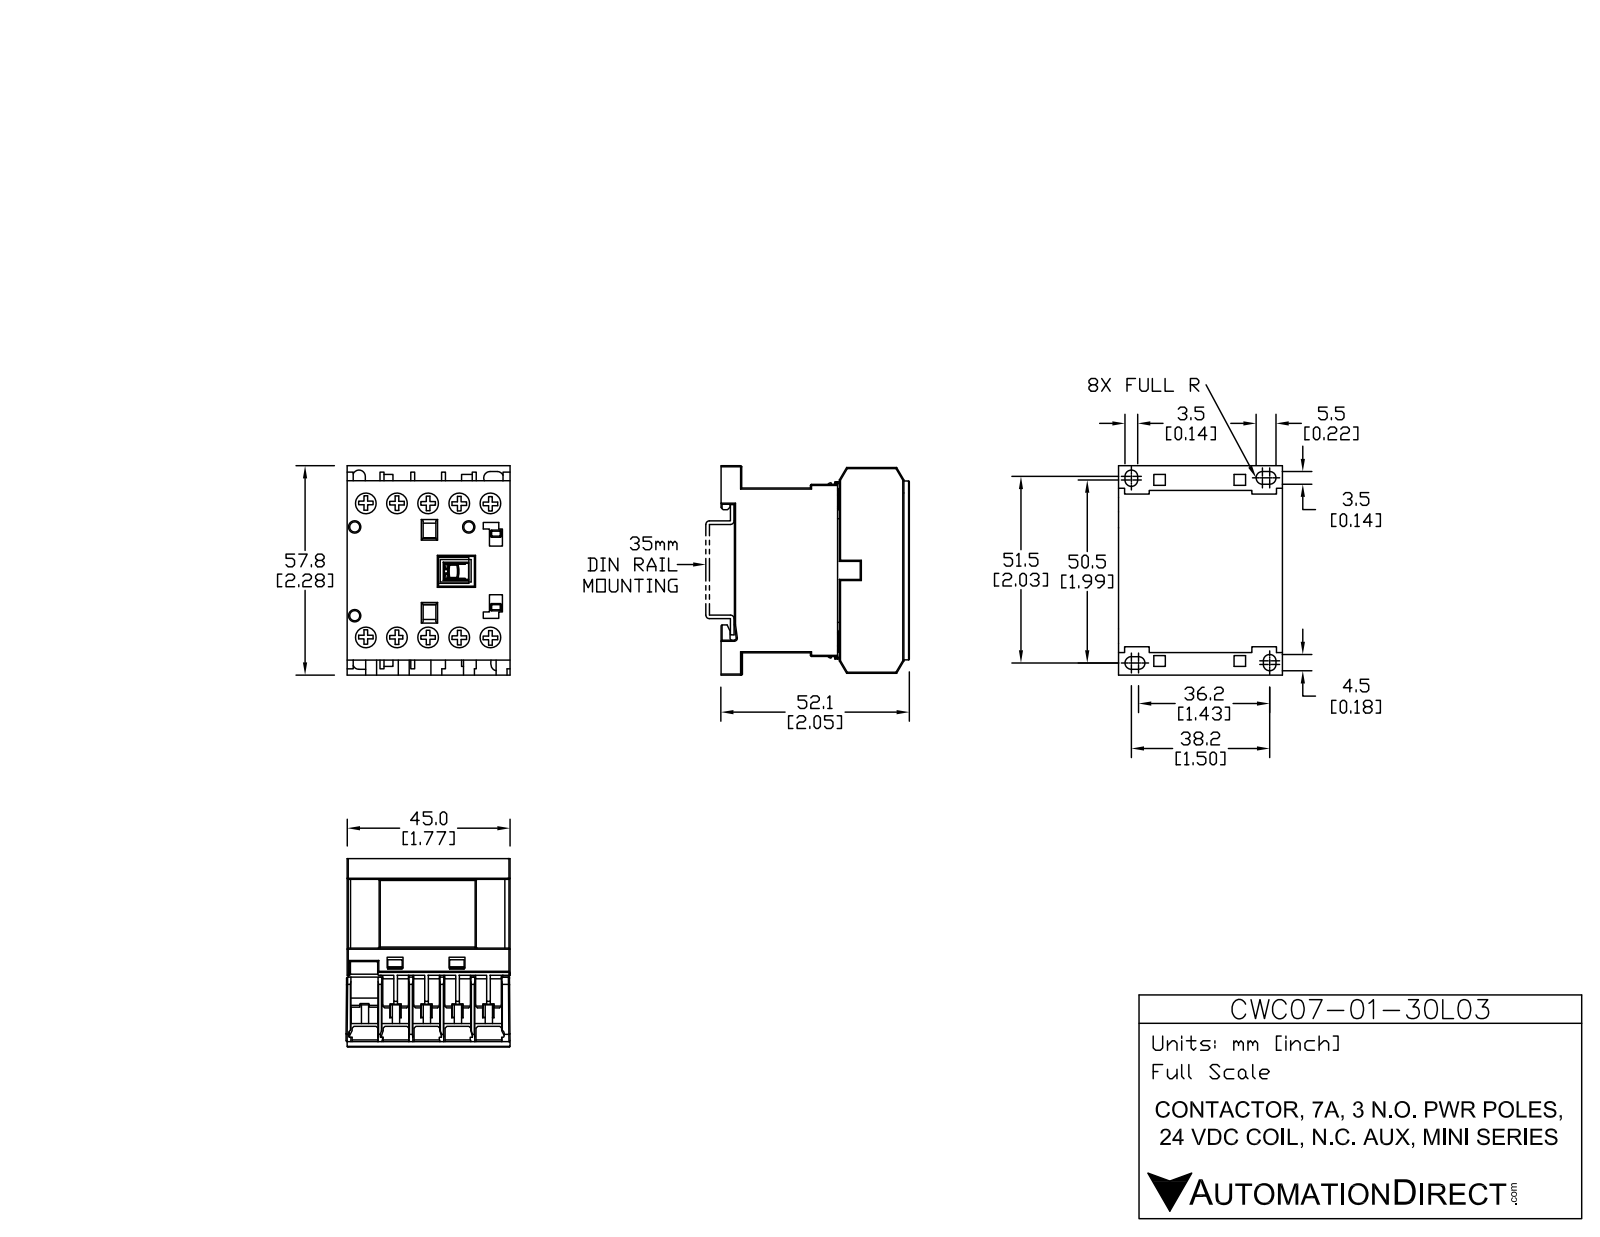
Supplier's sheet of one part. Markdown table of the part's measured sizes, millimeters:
| quantity | value |
| --- | --- |
| part name | CWC07-01-30L03 |
| STEP written by | SolidWorks 2013 (AUTOMOTIVE_DESIGN) |
| units | millimeters |
| bodies | 15 solids, 535 faces (445 planar, 90 cylindrical, 0 other) |
| overall size | 58.04 × 52.12 × 45.75 |
| volume | 97 133 mm³ |
| surface area | 30 437 mm² |
| round holes (diameter × count) | 6.2 × 10, 2.8 × 3 |
| round bosses / shafts (diameter × count) | 5.9 × 10 |
| partial cylindrical surfaces (radius × count) | 0.3 × 20, 1.72 × 6, 1.73 × 2, 0.32 × 1, 0.42 × 1, 0.55 × 1 |
| main face-to-face distances | 8.25, 45.5, 1.25, 16.5, 9.5, 5.5, 17.75, 5.13, 10.63, 7 |
| hole center spacings | 8.55, 37.94, 17.1, 40.72, 36.96, 25.65, 44.99, 6.91 |
